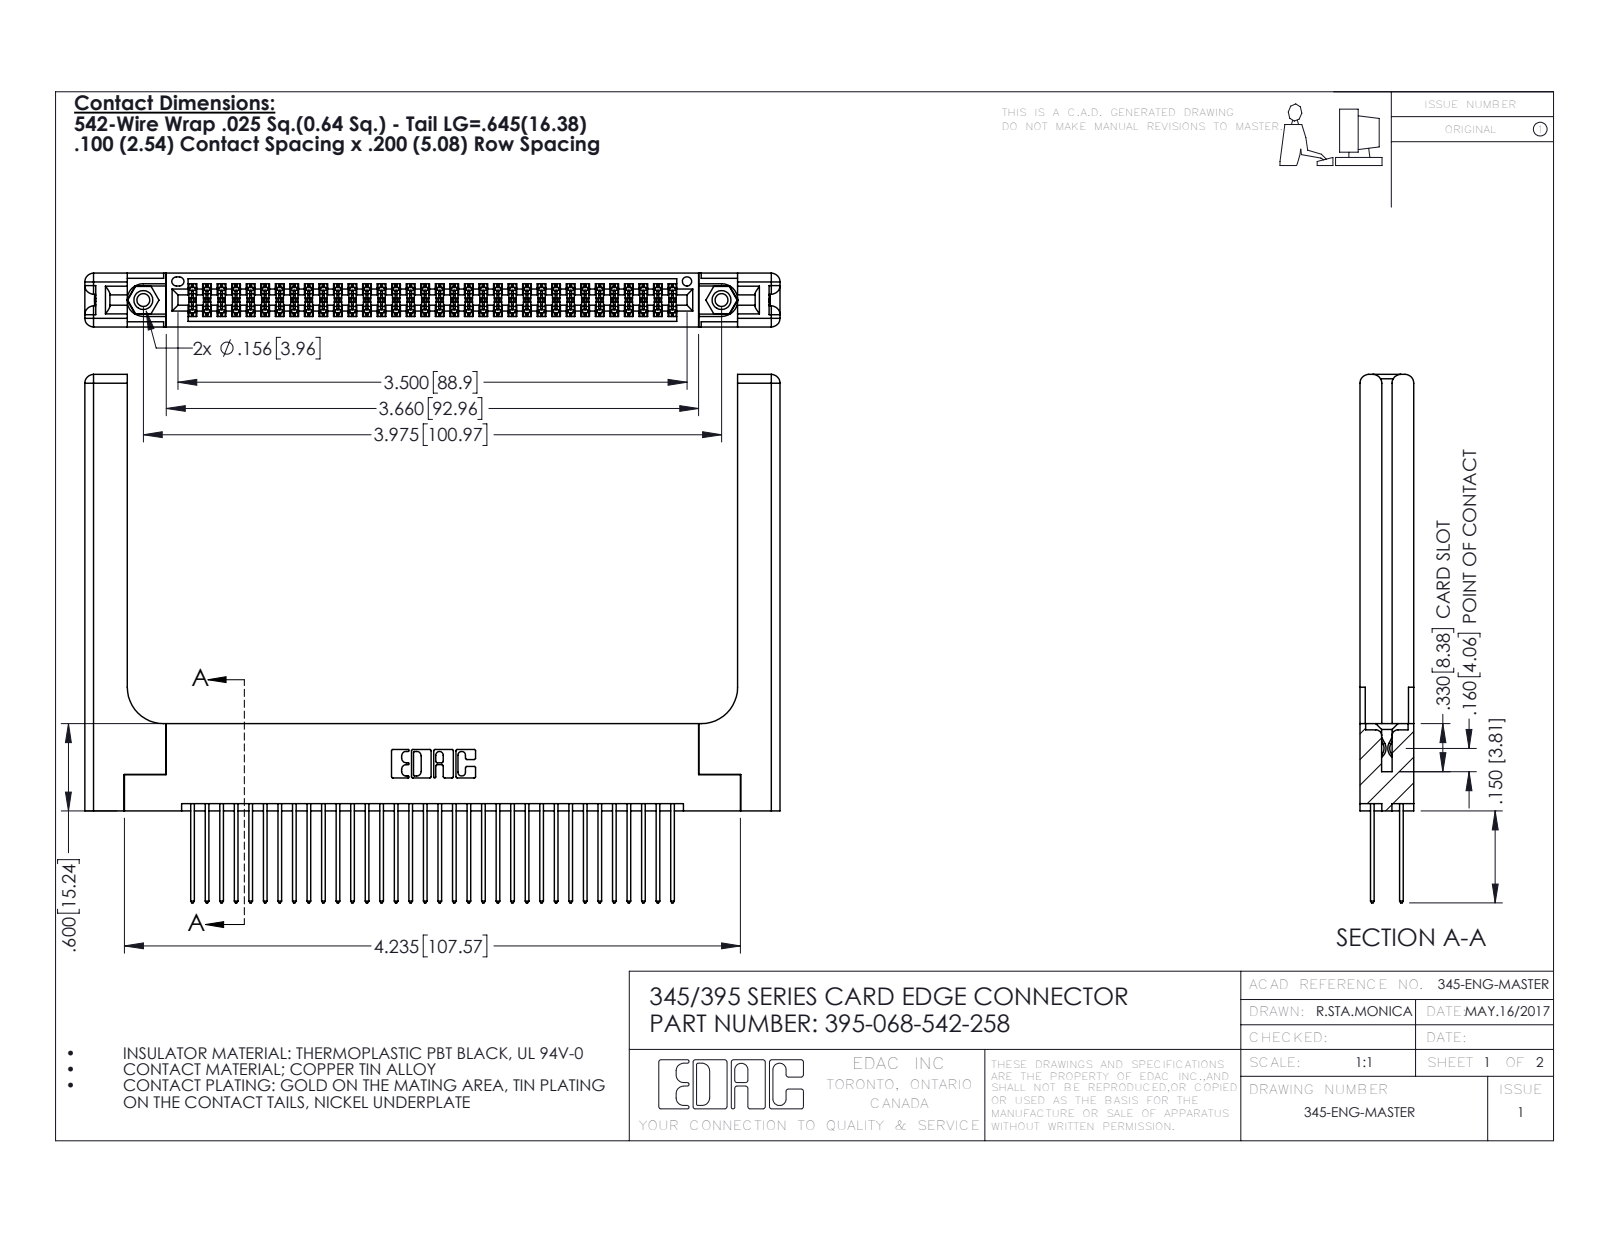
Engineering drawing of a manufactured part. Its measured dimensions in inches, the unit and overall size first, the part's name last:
Units: inches
Overall size (bounding box): 4.779 × 3.632 × 0.37
Round holes (diameter × count): ⌀0.089 ×2, ⌀0.125 ×2, ⌀0.156 ×2, ⌀0.064 ×1
Round bosses / shafts (diameter × count): ⌀0.155 ×2
Partial cylindrical surfaces — rounded edges, fillets, slot ends (radius × count): R0.006 ×102, R0.01 ×68, R0.01 ×22, R0.06 ×16, R0.007 ×6, R0.031 ×6, R0.026 ×3, R0.014 ×2
Main face-to-face distances: 0.072, 0.298, 0.37, 0.2, 0.098, 0.272, 0.025, 0.225, 0.148, 0.15
Hole centre spacings: 0.27, 3.74, 3.975
Volume: 1.252 in³ · Surface area: 37.47 in²
Bodies: 73 solids, 3782 faces (2472 planar, 1250 cylindrical, 60 other)
Part name (STEP PRODUCT): 395-068-542-258; 345-250-001_345-250-001-102; 345-292-001_345-293-142; 345-220-058_345-220-058 (+1 more)
STEP written by: SolidWorks 2016 (CONFIG_CONTROL_DESIGN)
